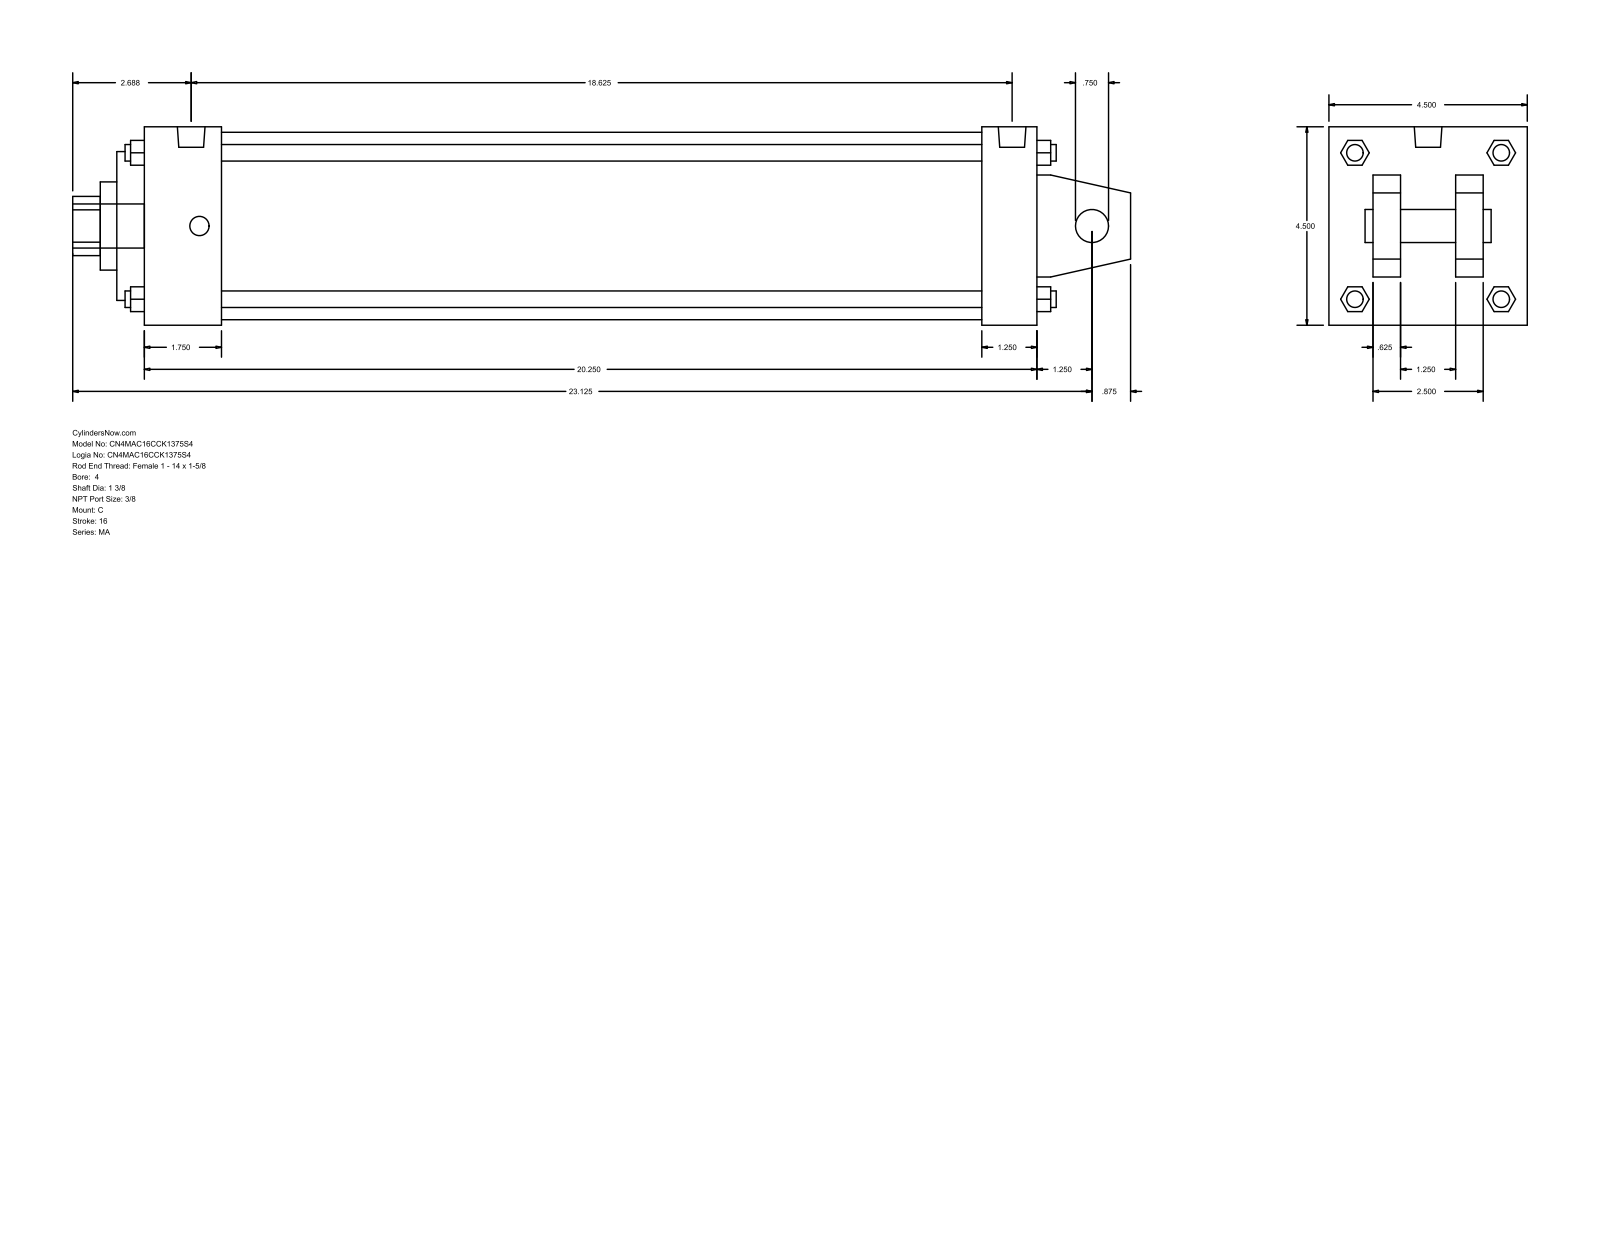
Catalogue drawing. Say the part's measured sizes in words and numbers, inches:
The part is named "MA_C__0400_1.375". Its 3-D file was written by "GSSL Pune (CONFIG_CONTROL_DESIGN)". It is 0 solids with 141 faces: 109 planar, 32 cylindrical and 0 other. Overall it measures 24 by 4.5 by 4.5 inches. Round holes: 1 of diameter 0.75, 1 of diameter 1.375, 1 of diameter 2, 1 of diameter 3.375, 1 of diameter 4.25. Round bosses or shafts: 4 of diameter 0.437, 4 of diameter 0.375, 2 of diameter 0.627, 1 of diameter 1. Partial cylindrical surfaces (rounded edges, fillets, slot ends): 1 of radius 0.672. The main face-to-face distances are 4.5, 0.625, 20.25, 2.875, 1.625, 1, 3.5, 1.875, 20.875, 19.625.
